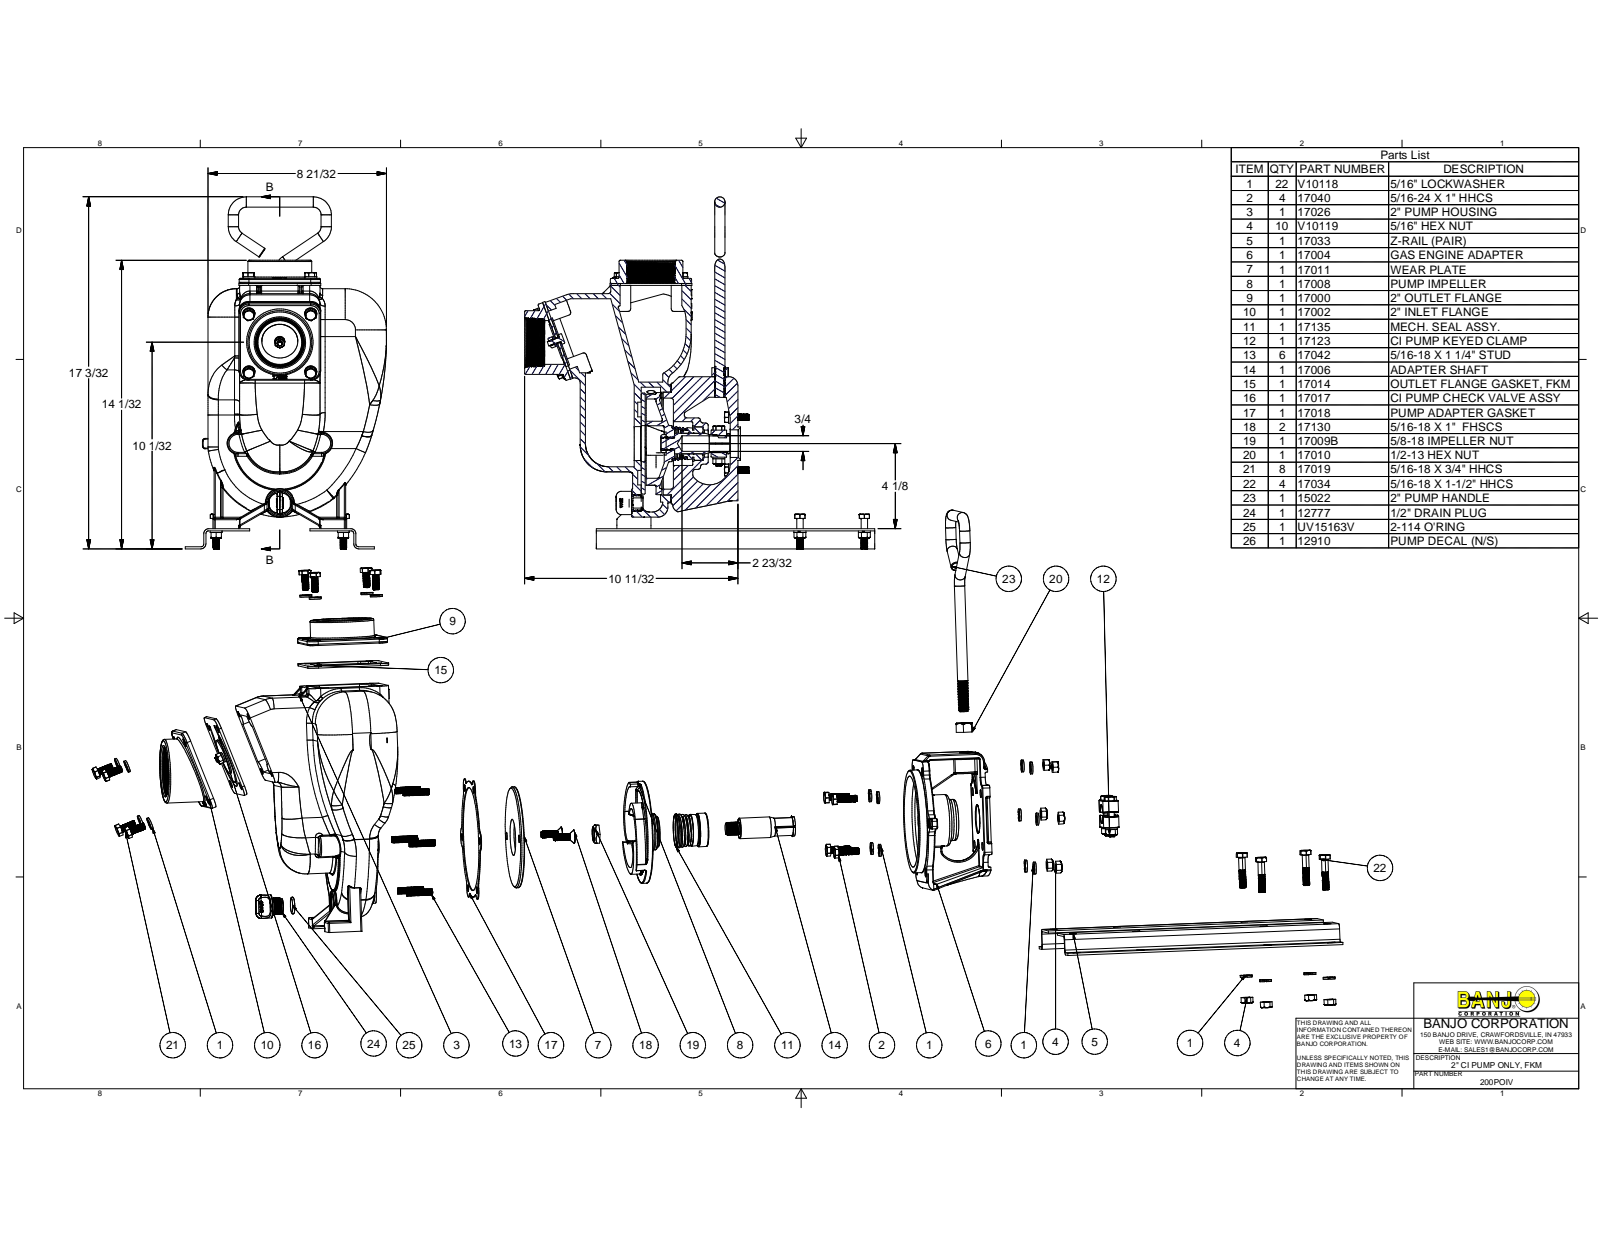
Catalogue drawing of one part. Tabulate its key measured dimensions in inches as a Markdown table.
| quantity | value |
| --- | --- |
| part name | 17026; 17004; V10118; 17040 (+8 more) |
| STEP written by | Autodesk Inventor 2014 (AUTOMOTIVE_DESIGN) |
| units | inches |
| bodies | 89 solids, 7183 faces (1286 planar, 2570 cylindrical, 3327 other) |
| overall size | 17.118 × 16.977 × 9.758 |
| round holes (diameter × count) | 0.322 × 24, 0.375 × 18, 0.252 × 17, 0.252 × 12, 0.344 × 8, 0.359 × 8, 0.313 × 6, 0.187 × 3, 0.196 × 2, 0.25 × 2, 0.35 × 2, 0.5 × 2 |
| round bosses / shafts (diameter × count) | 0.269 × 222, 0.276 × 92, 0.583 × 24, 0.313 × 20, 0.212 × 12, 0.246 × 6, 0.5 × 5, 3.094 × 2 |
| partial cylindrical surfaces (radius × count) | 0.06 × 129, 0.03 × 69, 0.25 × 46, 0.125 × 42, 0.02 × 22, 0.134 × 22, 0.5 × 22, 0.437 × 18 |
| main face-to-face distances | 0.105, 0.25, 0.875, 0.125, 3.65, 0.77, 1.777, 0.98, 0.337, 2.114 |
| hole center spacings | 3, 2.121, 2.813, 1.063, 7.233, 7.88, 2.122, 4.243 |
